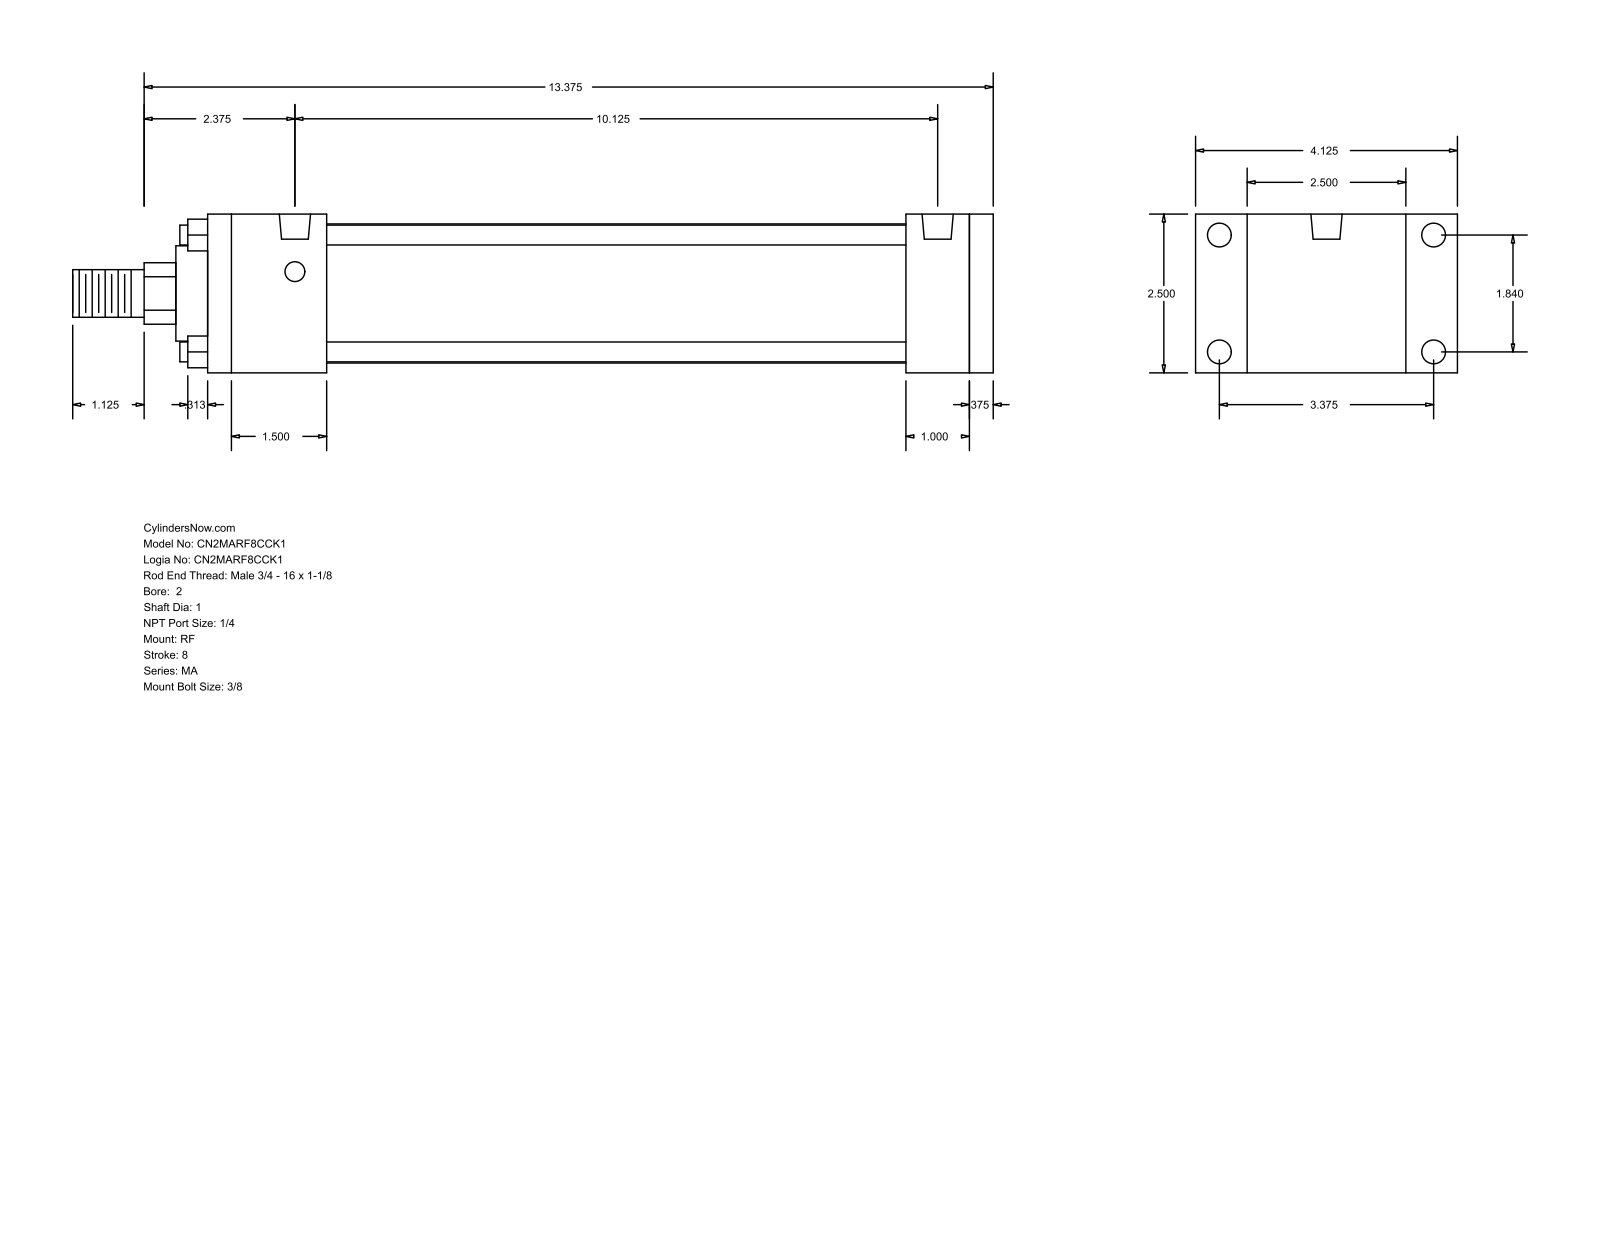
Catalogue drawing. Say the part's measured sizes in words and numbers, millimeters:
The part is named "MA_RF__0200_1". Its 3-D file was written by "GSSL Pune (CONFIG_CONTROL_DESIGN)". It is 0 solids with 92 faces: 64 planar, 28 cylindrical and 0 other. Overall it measures 368.3 by 104.78 by 63.5 millimeters. Round holes: 4 of diameter 7.94, 4 of diameter 9.53, 2 of diameter 12.49. Round bosses or shafts: 4 of diameter 7.94, 1 of diameter 55.63, 1 of diameter 38.1, 1 of diameter 25.4, 1 of diameter 19.05. Partial cylindrical surfaces (rounded edges, fillets, slot ends): 1 of radius 12.29. The main face-to-face distances are 63.5, 304.8, 9.53, 314.33, 25.4, 20.64, 12.7, 47.63, 257.17, 266.7. The hole center spacings are 46.74, 85.72, 97.63, 257.17.
